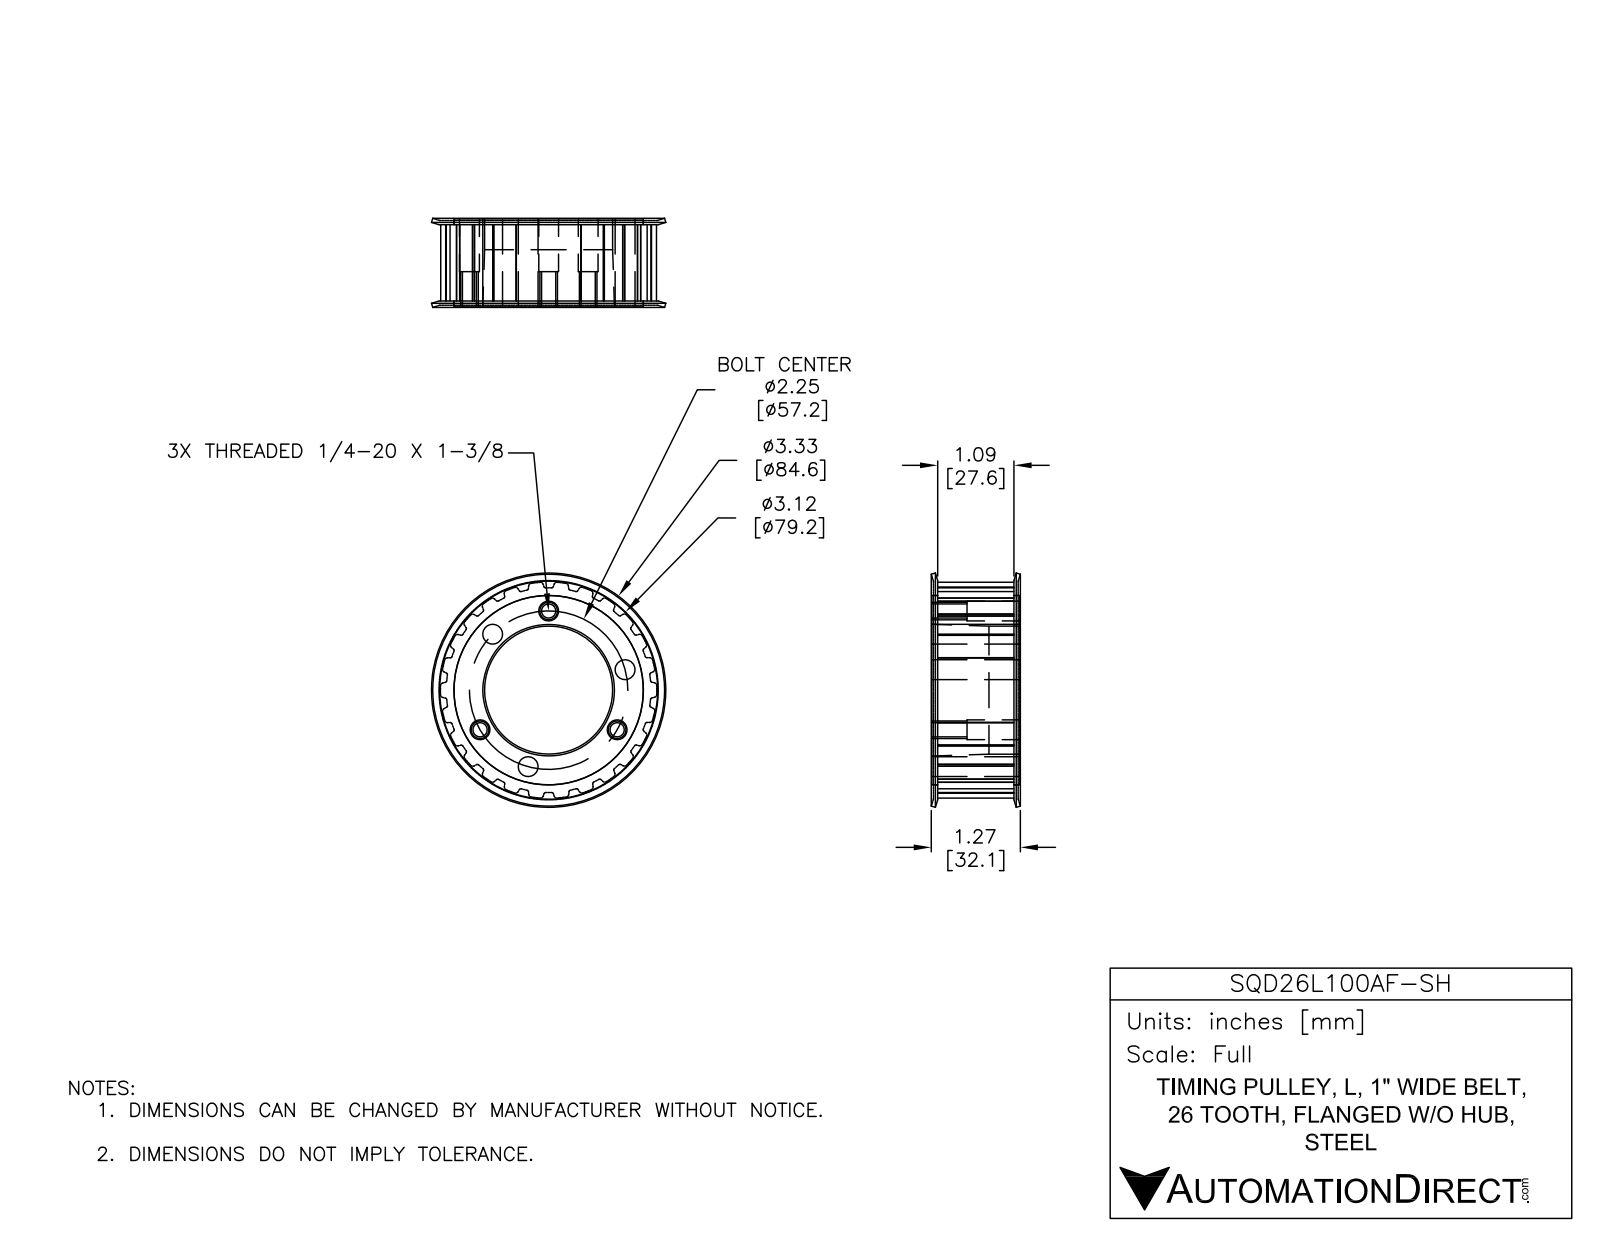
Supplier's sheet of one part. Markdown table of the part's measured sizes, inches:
| quantity | value |
| --- | --- |
| part name | SQD26L100AF-SH |
| STEP written by | SolidWorks 2018 (AUTOMOTIVE_DESIGN) |
| units | inches |
| bodies | 1 solid, 282 faces (89 planar, 179 cylindrical, 14 other) |
| overall size | 3.33 × 3.33 × 1.265 |
| volume | 5.264 in³ |
| surface area | 44.67 in² |
| round holes (diameter × count) | 0.281 × 6, 0.201 × 3, 1.82 × 1, 2.692 × 1 |
| round bosses / shafts (diameter × count) | 2.689 × 1 |
| partial cylindrical surfaces (radius × count) | 0.021 × 52, 0.04 × 52, 1.538 × 1 |
| main face-to-face distances | 0.022, 1.228, 1.25, 1.205, 1.168, 1.145, 0.06, 0.082, 0.083, 0.06 |
| hole center spacings | 1.125, 0.861, 1.948, 1.949, 2.231, 1.125, 1.37, 1.37 |
